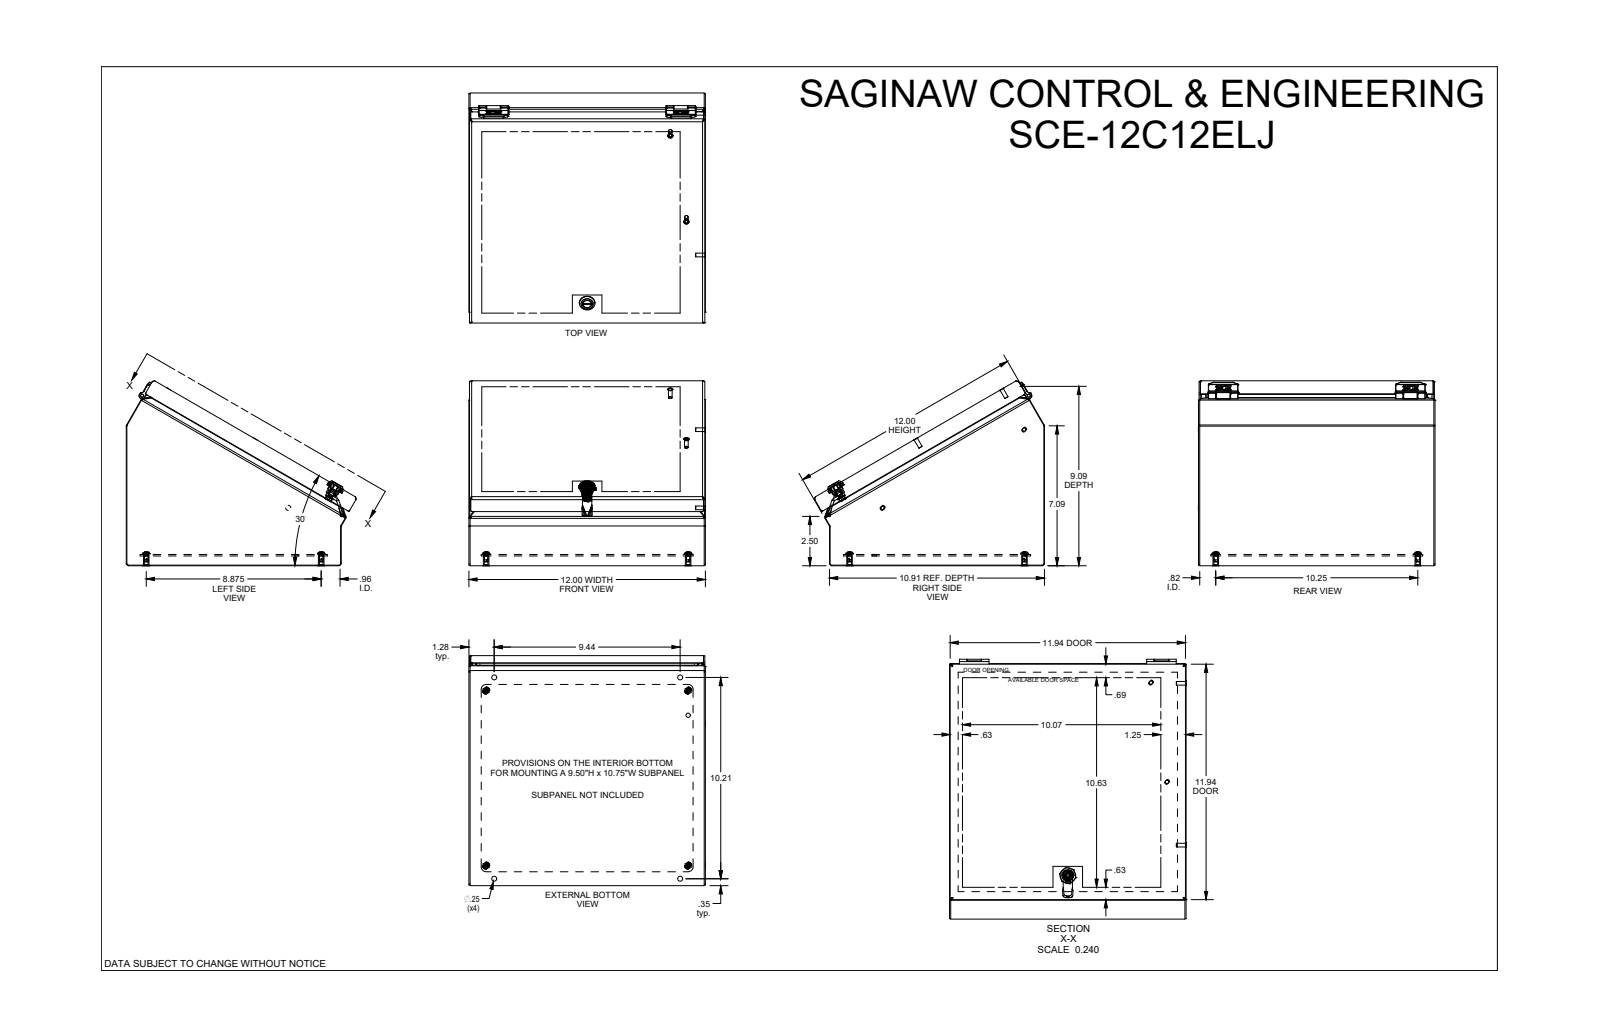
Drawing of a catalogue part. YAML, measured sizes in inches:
part_name: "SCE-12C12ELJ"
step_written_by: "SolidWorks 2019 (AUTOMOTIVE_DESIGN)"
units: inches
bodies: {solids: 26, faces: 964, planar: 382, cylindrical: 392, other: 190}
overall_size: [12.004, 11.665, 9.38]
volume: 48.06
surface_area: 1509
round_holes:
  - {diameter: 0.25, count: 8}
  - {diameter: 0.19, count: 4}
  - {diameter: 0.193, count: 4}
  - {diameter: 0.281, count: 4}
  - {diameter: 0.02, count: 2}
  - {diameter: 0.1, count: 2}
  - {diameter: 0.174, count: 2}
  - {diameter: 0.266, count: 2}
  - {diameter: 0.158, count: 1}
  - {diameter: 0.188, count: 1}
  - {diameter: 0.2, count: 1}
  - {diameter: 0.218, count: 1}
round_bosses_or_shafts:
  - {diameter: 0.28, count: 4}
  - {diameter: 0.256, count: 4}
  - {diameter: 0.188, count: 4}
  - {diameter: 0.26, count: 2}
  - {diameter: 0.18, count: 2}
  - {diameter: 0.788, count: 1}
  - {diameter: 0.548, count: 1}
  - {diameter: 0.46, count: 1}
partial_cylinders:
  - {radius: 0.03, count: 24}
  - {radius: 0.06, count: 22}
  - {radius: 0.013, count: 21}
  - {radius: 0.015, count: 20}
  - {radius: 0.12, count: 16}
  - {radius: 0.01, count: 14}
  - {radius: 0.02, count: 9}
  - {radius: 0.2, count: 6}
face_to_face_distances: [0.06, 0.06, 11.94, 0.436, 0.496, 0.075, 0.511, 0.571, 12, 11.88]
hole_center_spacings: [0.78, 9.549, 9.867, 13.709, 8.875, 9.438, 9.5, 10.206]
